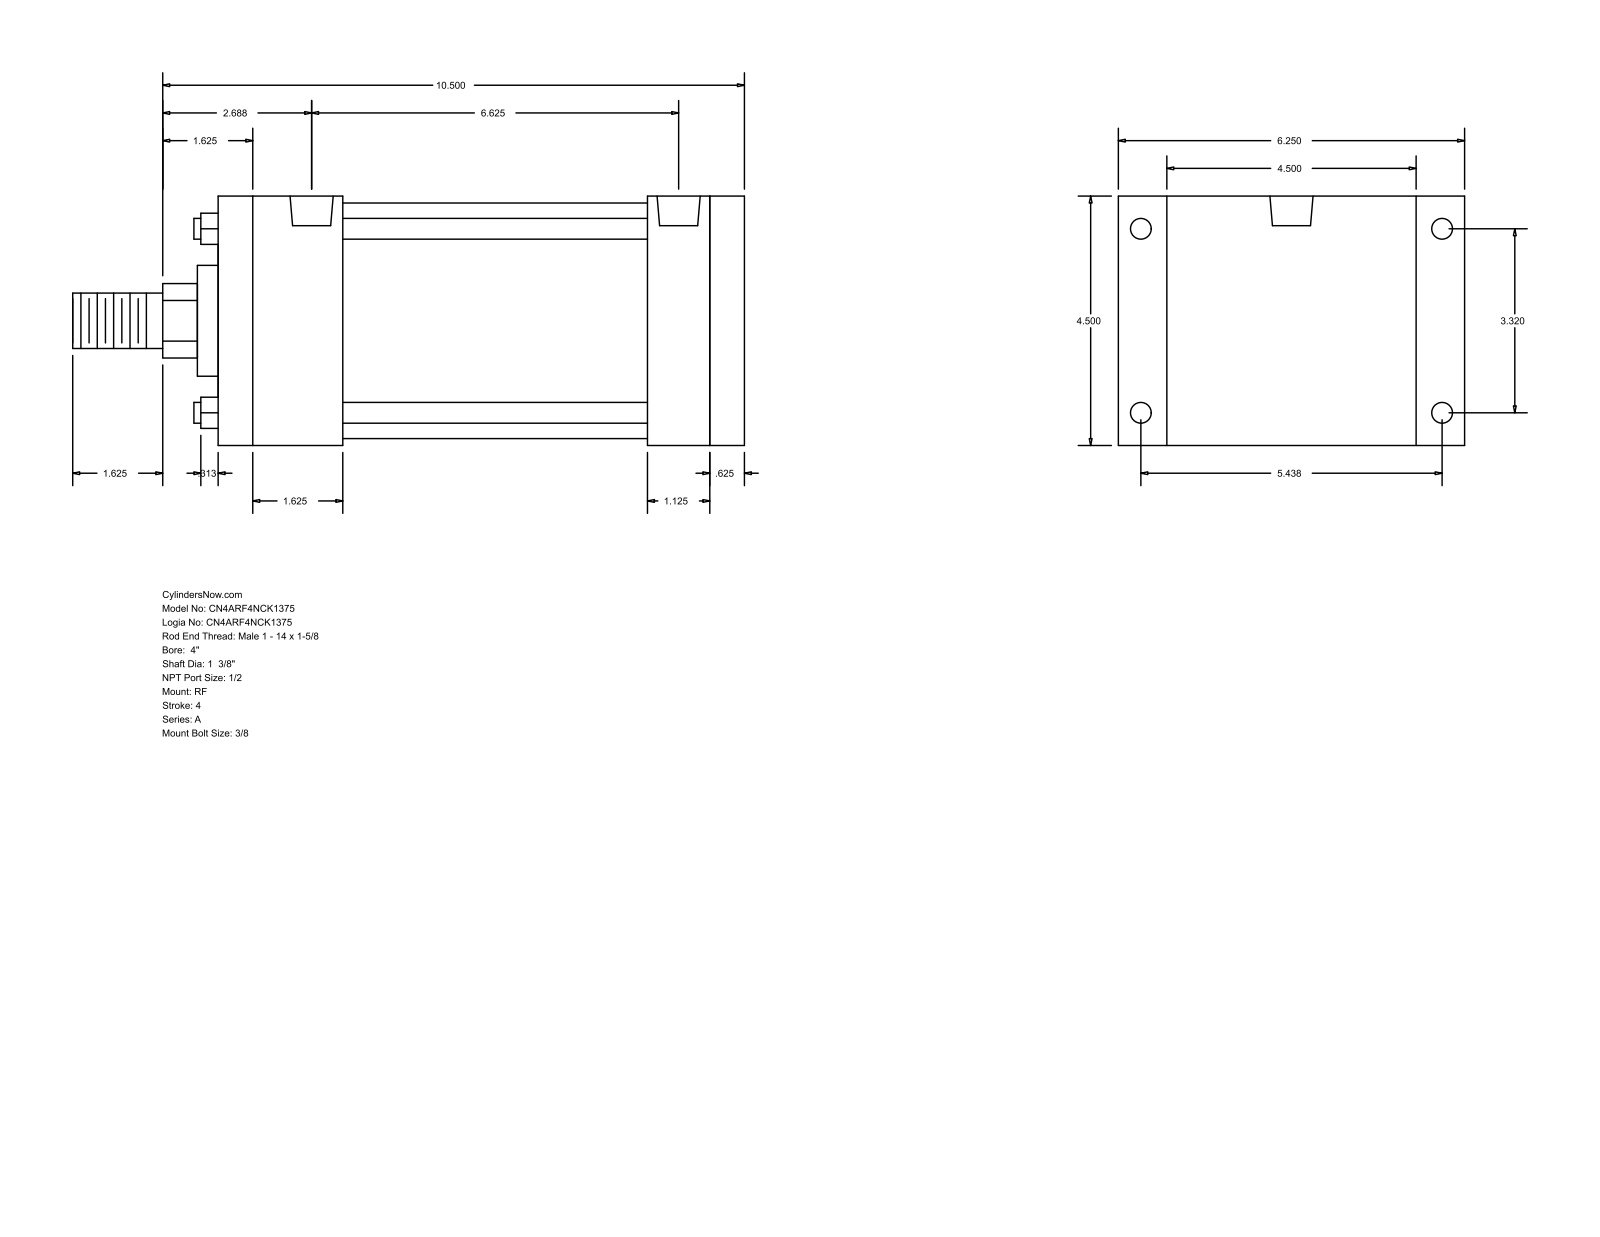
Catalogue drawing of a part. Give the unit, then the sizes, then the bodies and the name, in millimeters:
Units: millimetres
Overall size (bounding box): 307.98 × 158.75 × 114.3
Round holes (diameter × count): ⌀8.73 ×4, ⌀9.53 ×4, ⌀19.77 ×2
Round bosses / shafts (diameter × count): ⌀9.53 ×4, ⌀107.95 ×1, ⌀50.8 ×1, ⌀34.92 ×1, ⌀25.4 ×1
Partial cylindrical surfaces — rounded edges, fillets, slot ends (radius × count): R17.06 ×1
Main face-to-face distances: 114.3, 241.3, 15.88, 225.42, 57.15, 22.23, 136.53, 196.85, 28.57, 44.45
Hole centre spacings: 3.18, 84.32, 138.12, 161.82, 161.92, 165.1, 168.28
Bodies: 0 solids, 92 faces (64 planar, 28 cylindrical, 0 other)
Part name (STEP PRODUCT): A_RF__0400_1.375
STEP written by: GSSL Pune (CONFIG_CONTROL_DESIGN)
